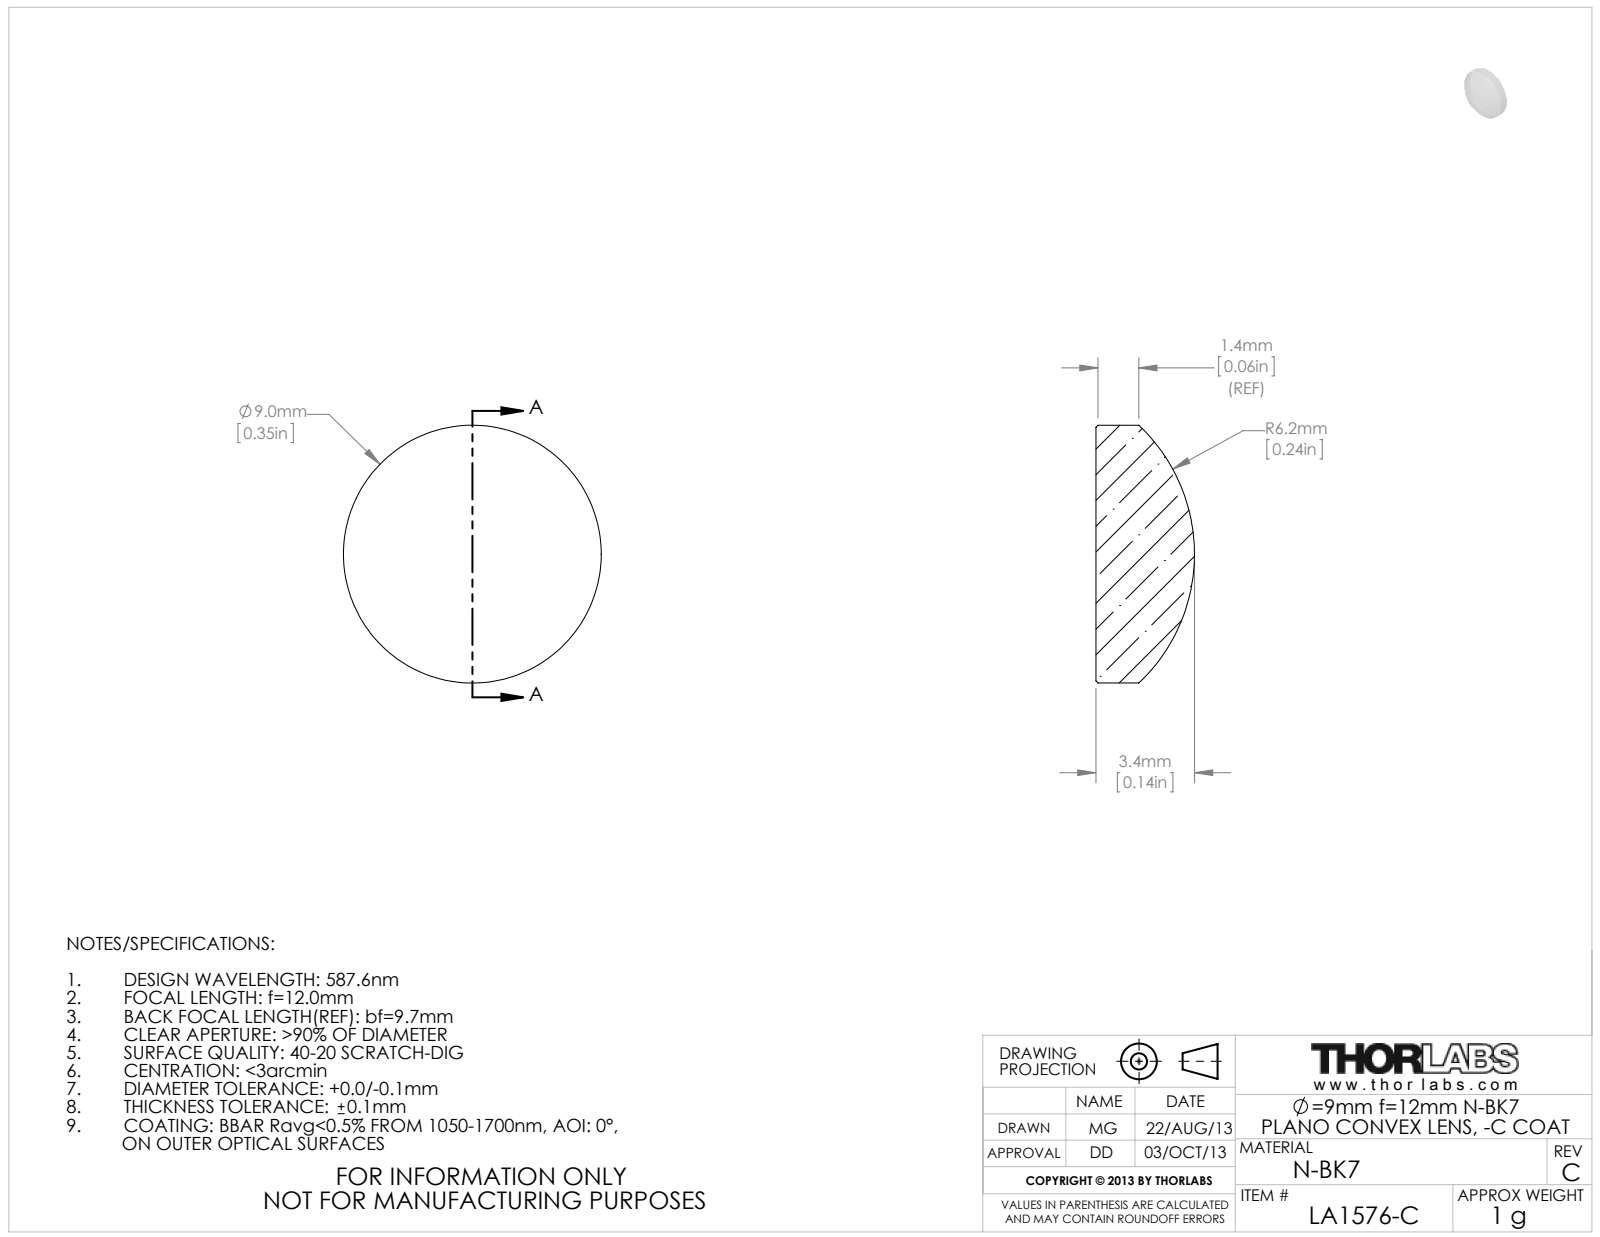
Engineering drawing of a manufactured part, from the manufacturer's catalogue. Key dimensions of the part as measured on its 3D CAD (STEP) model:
Part name (STEP PRODUCT): 4566-E0W
STEP written by: SolidWorks 2009 (AUTOMOTIVE_DESIGN)
Units: millimetres
Bodies: 1 solid, 5 faces (1 planar, 2 cylindrical, 2 other)
Overall size (bounding box): 9 × 9 × 3.44
Volume: 161 mm³ · Surface area: 181 mm²
Round bosses / shafts (diameter × count): ⌀9 ×1
